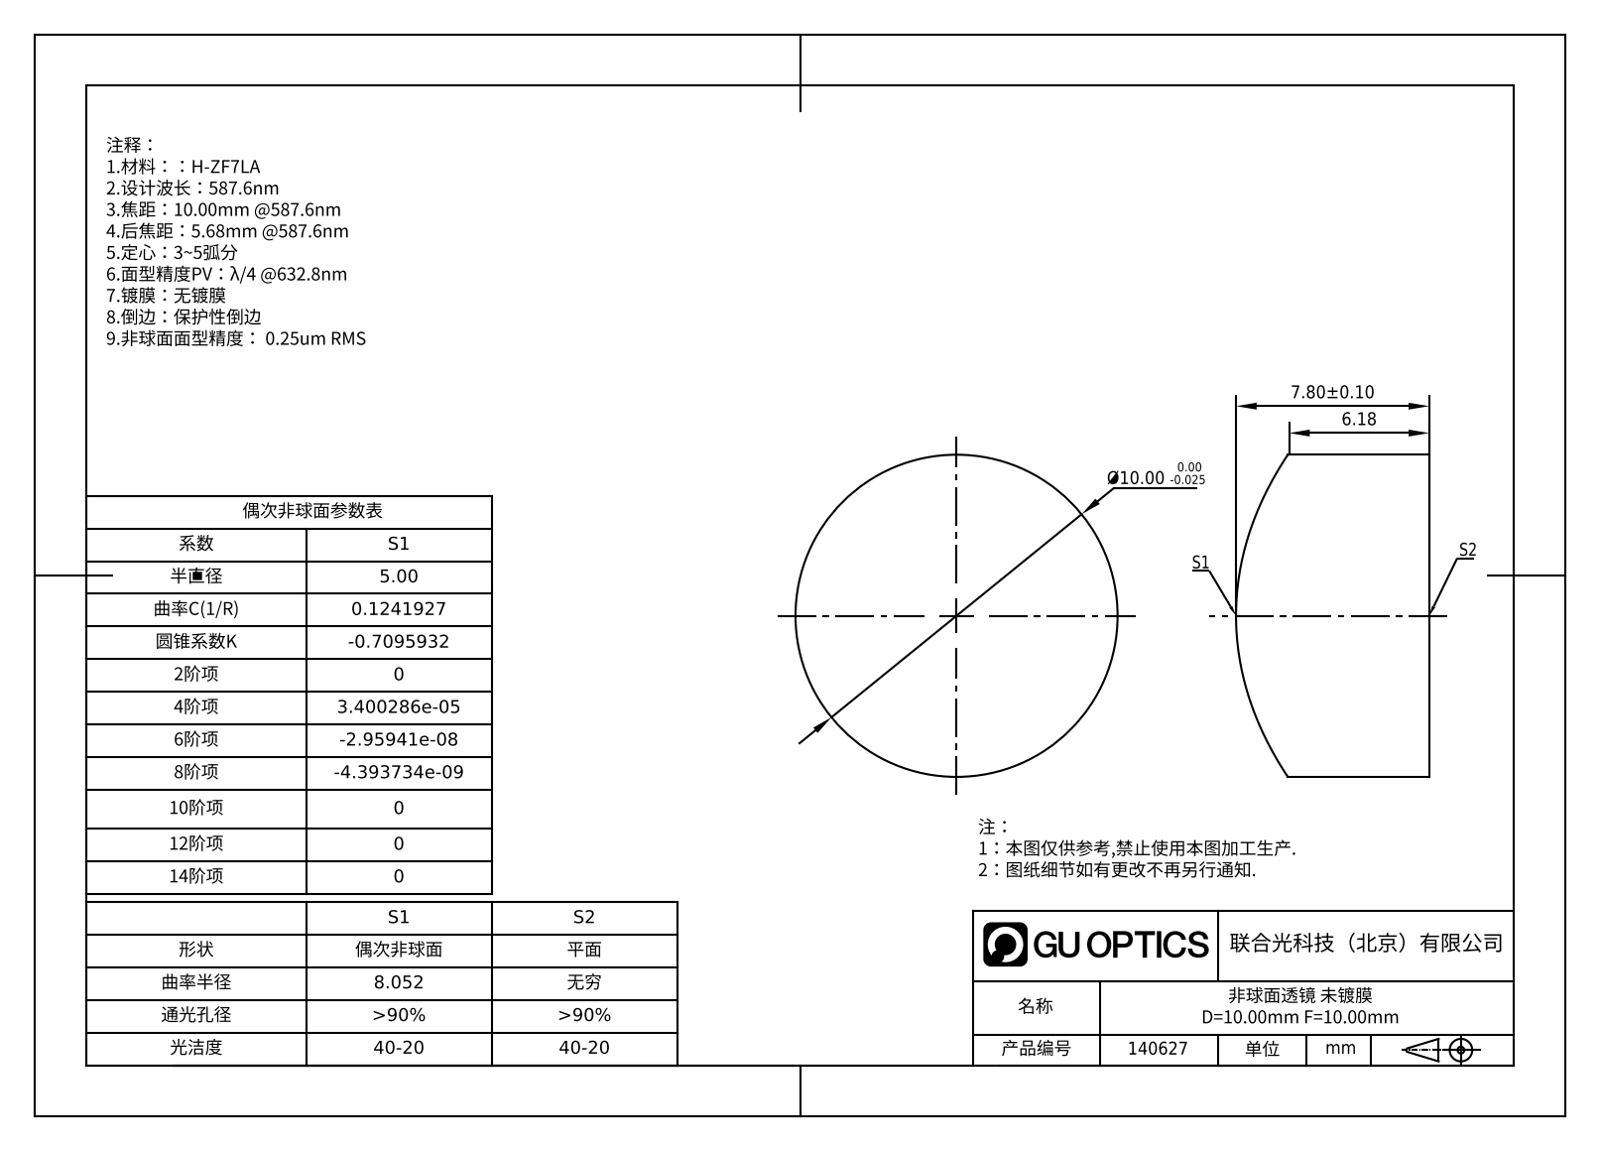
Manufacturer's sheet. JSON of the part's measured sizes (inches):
{"part_name": "surfaces 1,2.stp; GLA11-010-010-H.stp; GLA11-010-010-H", "step_written_by": "SolidWorks 2023 (CONFIG_CONTROL_DESIGN)", "units": "inches", "bodies": {"solids": 1, "faces": 5, "planar": 1, "cylindrical": 2, "other": 2}, "overall_size": [0.394, 0.394, 0.307], "volume_in3": 0.034, "surface_area_in2": 0.556, "round_bosses_or_shafts": [[0.394, 1]]}
